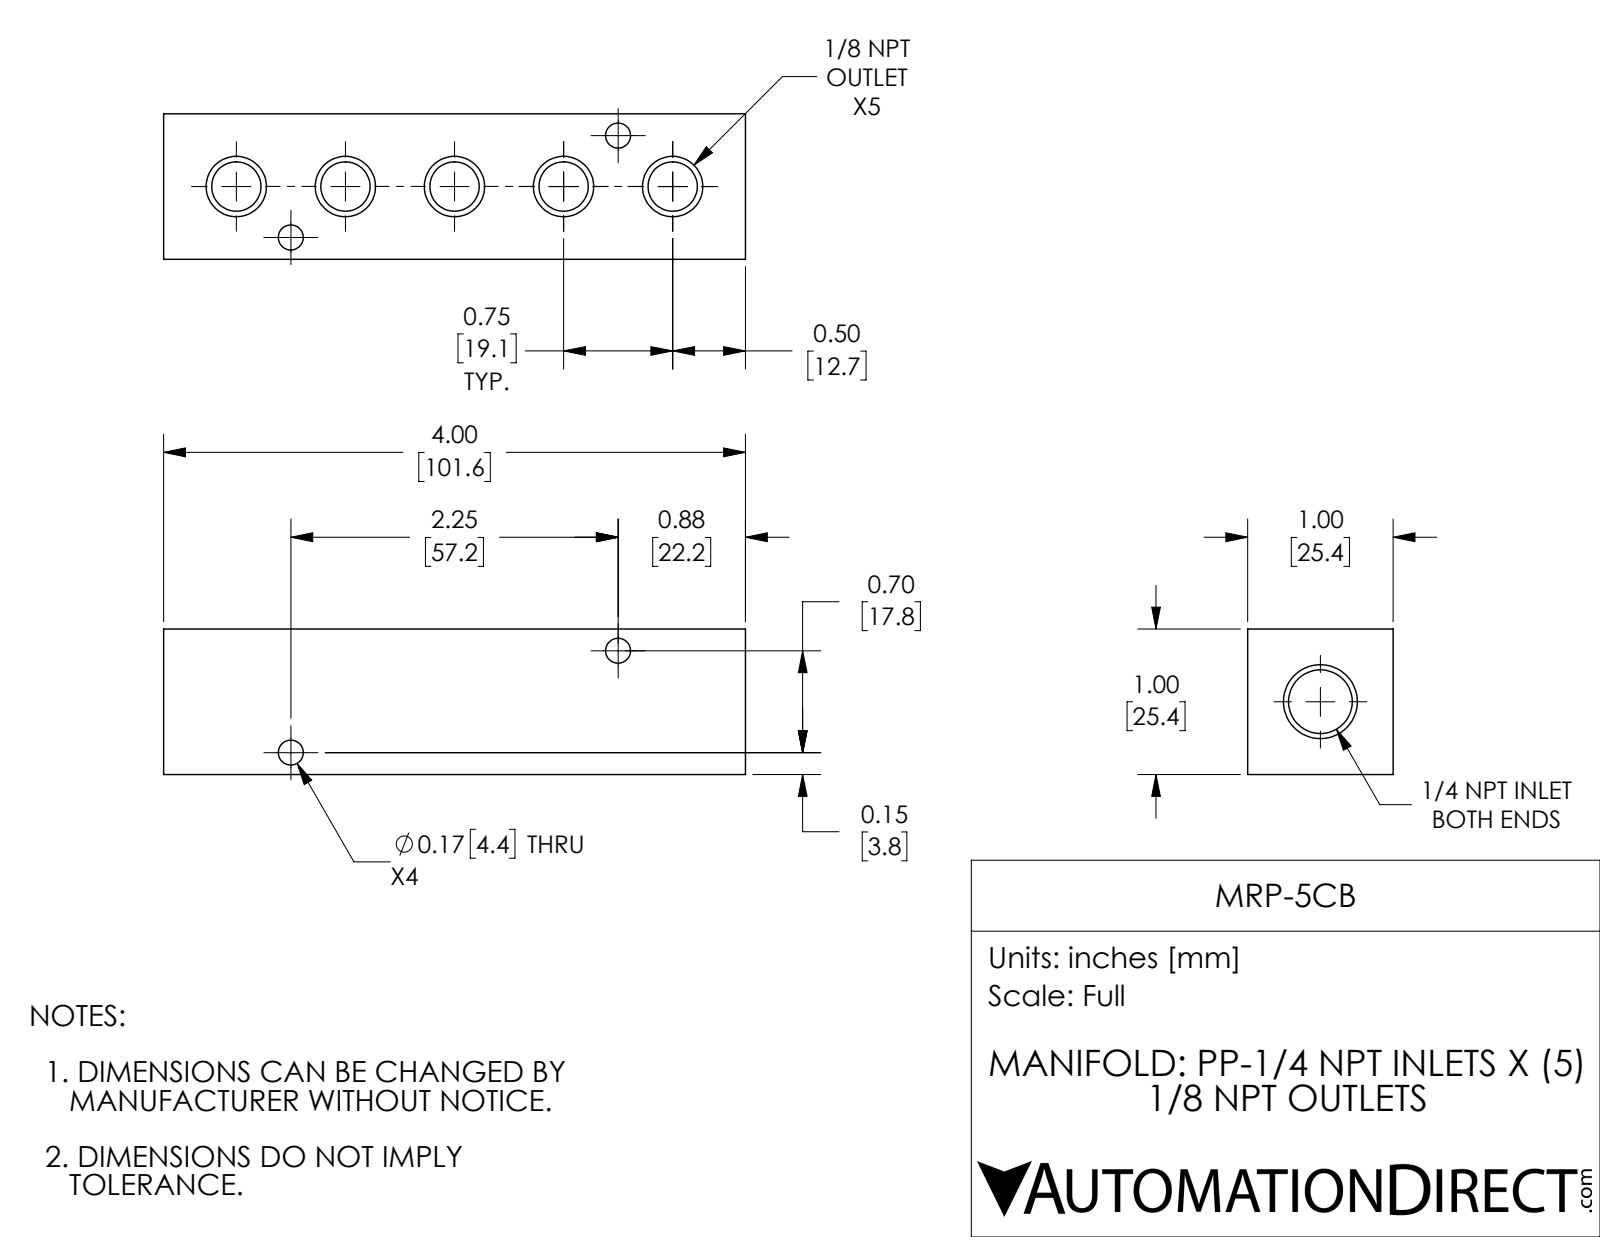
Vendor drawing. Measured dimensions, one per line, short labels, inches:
name: MRP-5CB
written by: SolidWorks 2018 (AUTOMOTIVE_DESIGN)
unit: in
bodies: 1 solid, 48 faces (6 planar, 28 cylindrical, 14 other)
size: 4 × 1 × 1
volume: 3.17 in³; area: 25.53 in²
holes: 5× ⌀0.339, 4× ⌀0.172, 1× ⌀0.438
face distances: 1, 4
hole spacings: 0.513, 0.75, 1.5, 1.178, 1.907, 2.25, 2.357, 2.648
